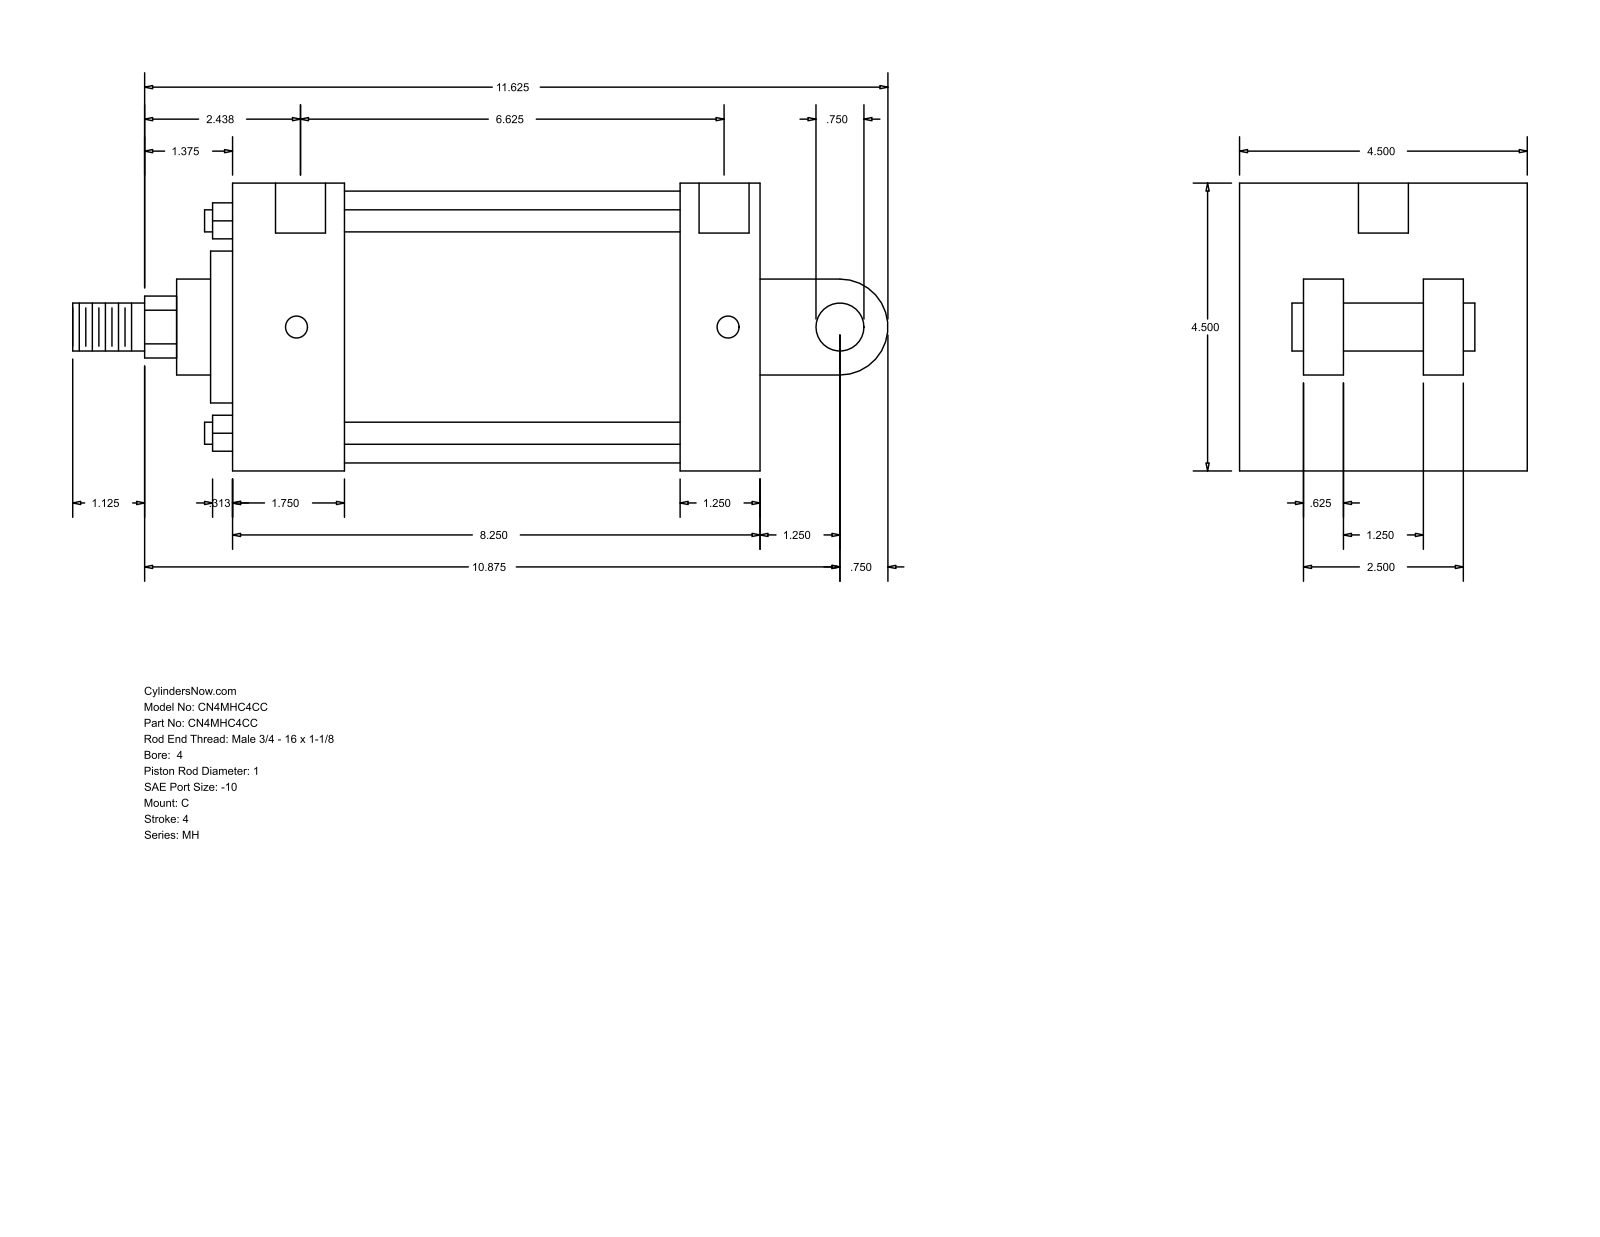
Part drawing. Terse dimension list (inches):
name: MH_C__0400_1
written by: GSSL Pune (CONFIG_CONTROL_DESIGN)
unit: in
bodies: 0 solids, 101 faces (71 planar, 30 cylindrical, 0 other)
size: 12.75 × 4.5 × 4.5
holes: 4× ⌀0.344, 2× ⌀0.781
bosses: 4× ⌀0.345, 2× ⌀0.75, 1× ⌀4.25, 1× ⌀2.375, 1× ⌀1.5, 1× ⌀1
rounds: 1× R0.484, 1× R0.75
face distances: 4.5, 8.25, 1.75, 7, 5.25, 6.5, 1.25, 2.875, 1.625, 1.5
hole spacings: 6.75, 0.062, 0.063, 6.625, 6.687, 6.688
